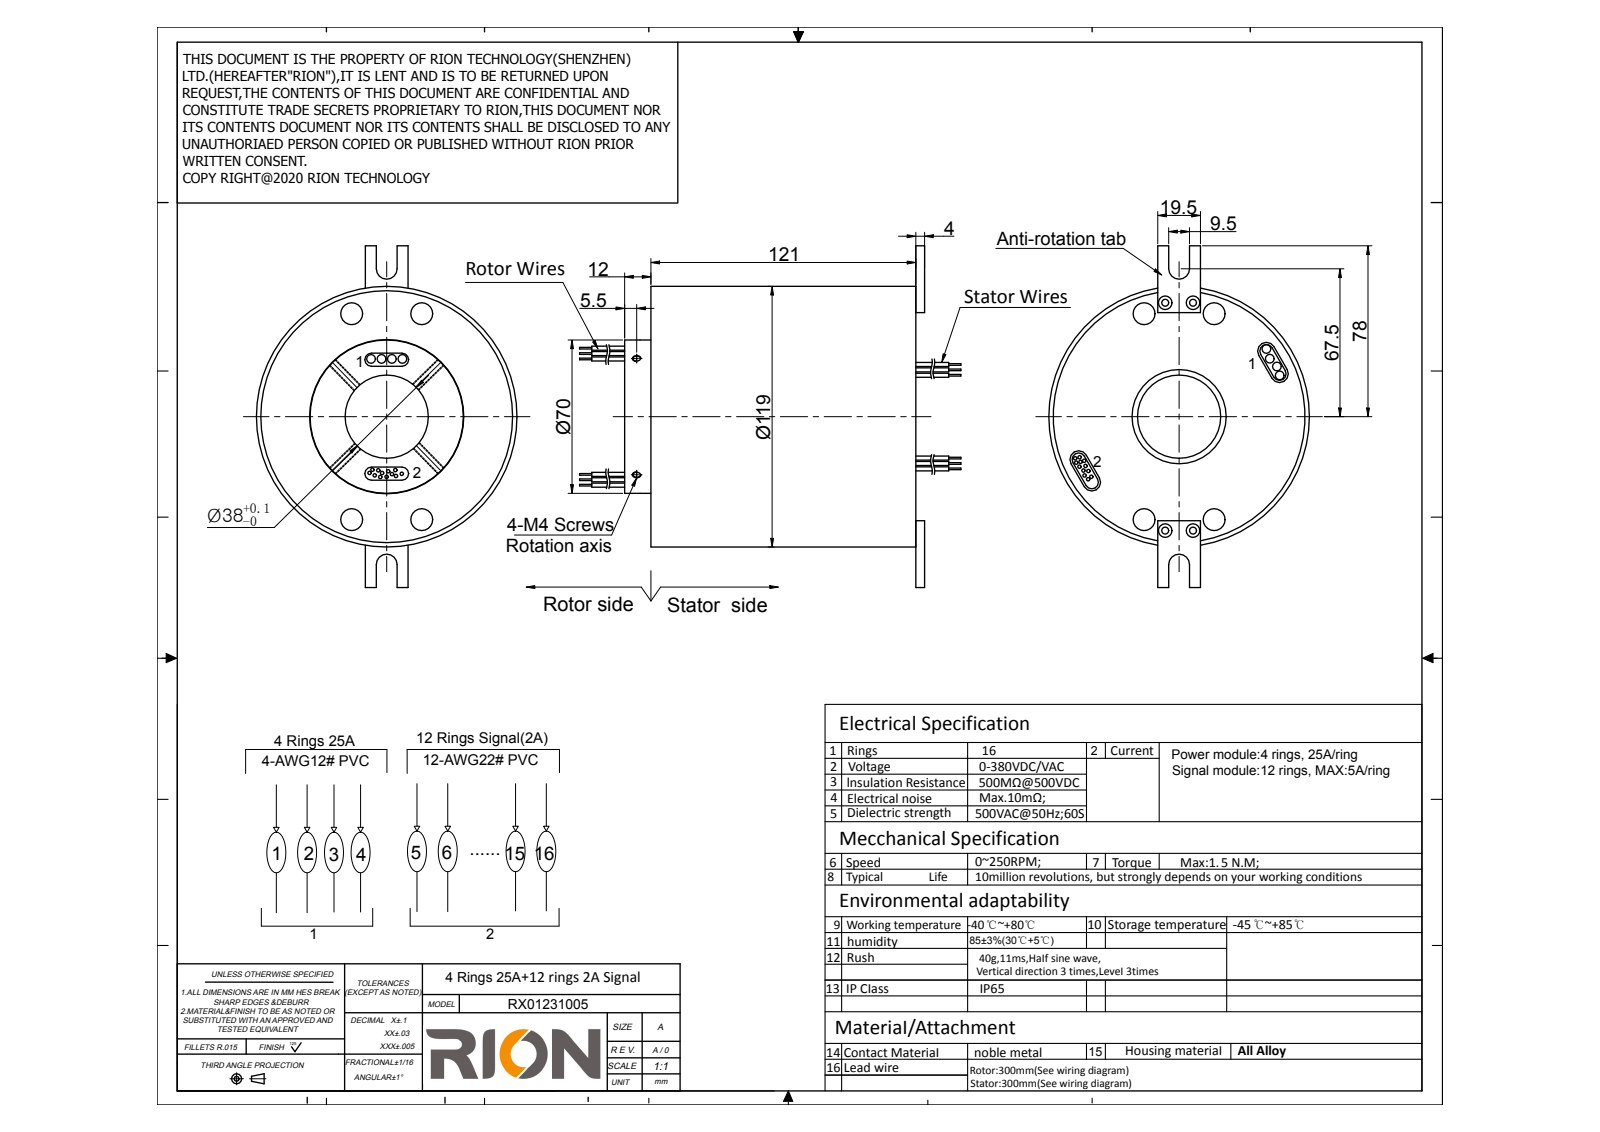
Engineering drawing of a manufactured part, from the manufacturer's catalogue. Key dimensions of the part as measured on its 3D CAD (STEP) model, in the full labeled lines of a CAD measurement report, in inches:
Part name (STEP PRODUCT): RX01231005
STEP written by: SolidWorks 2014 (CONFIG_CONTROL_DESIGN)
Units: inches
Bodies: 1 solid, 214 faces (74 planar, 124 cylindrical, 16 other)
Overall size (bounding box): 6.732 × 6.142 × 4.685
Volume: 76.04 in³ · Surface area: 150.4 in²
Round holes (diameter × count): ⌀0.098 ×4, ⌀0.126 ×4, ⌀0.13 ×4, ⌀1.496 ×1, ⌀2.126 ×1, ⌀4.528 ×1
Round bosses / shafts (diameter × count): ⌀0.063 ×24, ⌀0.157 ×8, ⌀4.685 ×1, ⌀4.52 ×1, ⌀2.756 ×1, ⌀2.118 ×1
Partial cylindrical surfaces — rounded edges, fillets, slot ends (radius × count): R0.118 ×4, R0.138 ×4, R0.187 ×2, R0.915 ×1, R1.151 ×1
Main face-to-face distances: 4.764, 0.472, 5.236, 5.394, 4.921, 0.157, 0.039, 5.197, 0.768, 0.197
Hole centre spacings: 2.063, 0.5, 4.094, 4.125
